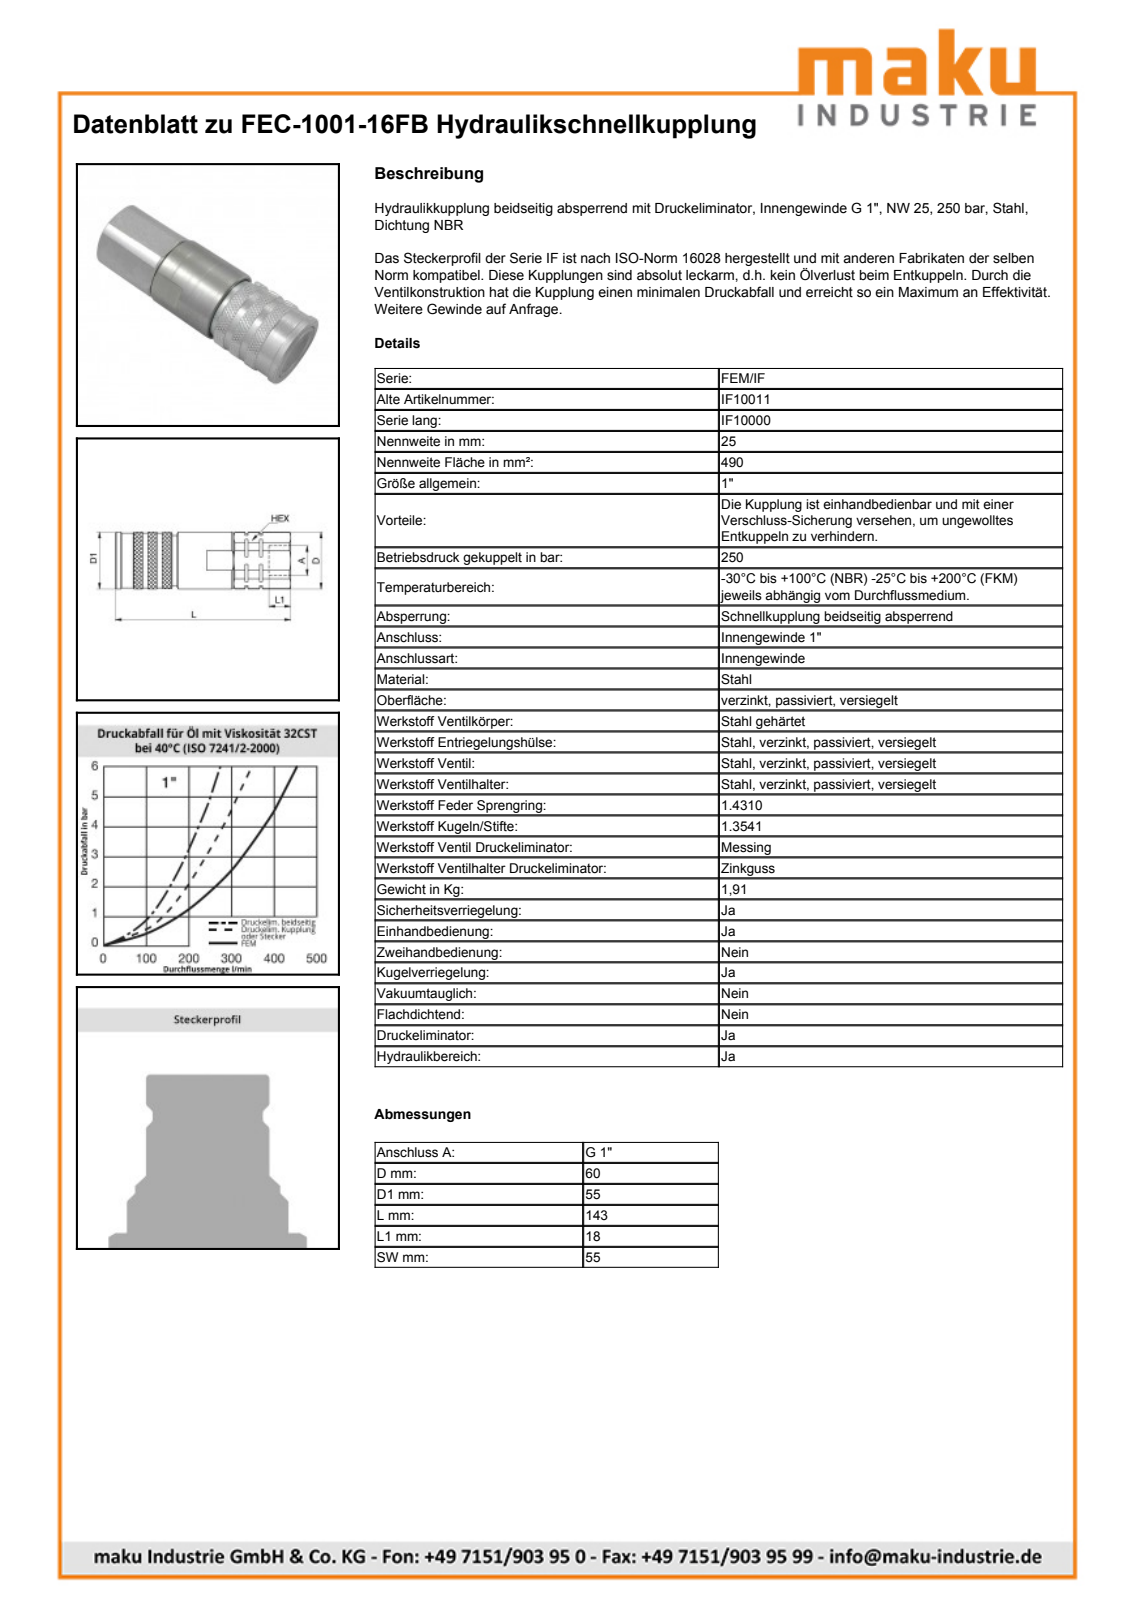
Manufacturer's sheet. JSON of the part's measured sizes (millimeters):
{"part_name": "FEC-1001-16FB", "step_written_by": "SolidWorks 2009 (AUTOMOTIVE_DESIGN)", "units": "millimeters", "bodies": {"solids": 1, "faces": 254, "planar": 84, "cylindrical": 81, "other": 89}, "overall_size": [142.85, 60, 55], "volume_mm3": 319376, "surface_area_mm2": 40672, "round_holes": [[1.5, 1], [3, 1], [9.22, 1], [23.7, 1], [29, 1], [30.3, 1], [34.2, 1], [36.1, 1], [45.35, 1], [50, 1], [50.3, 1]], "round_bosses_or_shafts": [[55, 1], [54, 1], [52.49, 1], [49.7, 1], [46, 1], [45.15, 1], [35.9, 1], [23.5, 1]], "partial_cylinders_radius": [[0.5, 8], [0.6, 2], [6, 1], [14.55, 1], [22.44, 1], [30, 1]], "face_to_face_distances": [55, 142.85, 142.35, 0.5, 2.5, 52.5, 28.7, 113.65, 114.15, 139.98]}
